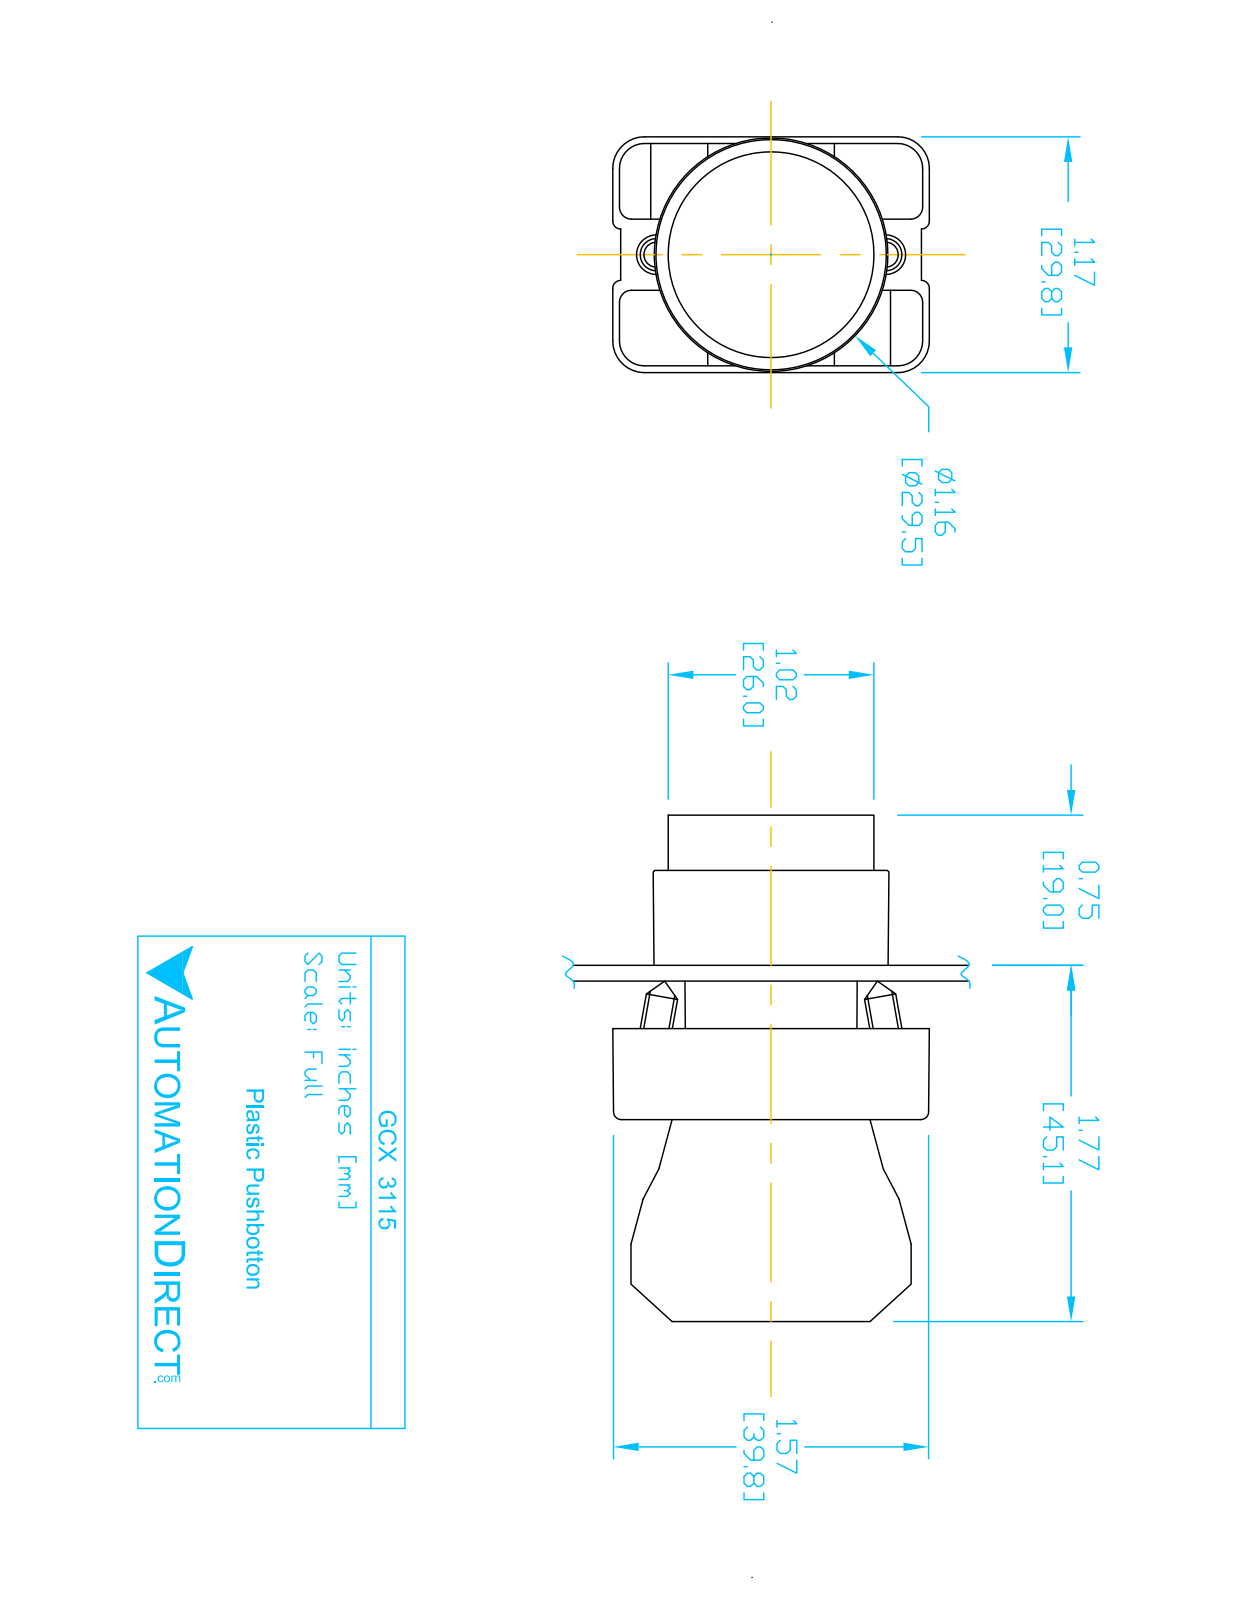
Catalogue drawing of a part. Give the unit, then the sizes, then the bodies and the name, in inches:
Units: inches
Overall size (bounding box): 2.492 × 1.581 × 1.177
Round holes (diameter × count): ⌀0.079 ×2, ⌀0.124 ×2, ⌀0.13 ×2, ⌀0.087 ×1, ⌀0.197 ×1, ⌀0.878 ×1, ⌀0.888 ×1, ⌀1.024 ×1
Round bosses / shafts (diameter × count): ⌀0.157 ×2, ⌀1.175 ×1, ⌀1.004 ×1, ⌀0.945 ×1, ⌀0.856 ×1, ⌀0.78 ×1
Partial cylindrical surfaces — rounded edges, fillets, slot ends (radius × count): R0.059 ×24, R0.041 ×12, R0.124 ×12, R0.157 ×12, R0.039 ×4, R0.128 ×2, R0.02 ×1, R0.063 ×1
Main face-to-face distances: 0.579, 0.033, 1.193, 0.031, 0.472, 0.72, 0.276, 0.689, 0.598, 1.161
Hole centre spacings: 0.236, 0.544, 0.472, 0.49
Volume: 1.584 in³ · Surface area: 26.47 in²
Bodies: 6 solids, 383 faces (222 planar, 132 cylindrical, 29 other)
Part name (STEP PRODUCT): ECX3029-2; ecx1040; GCX3115 OPERATOR; GCX3115
STEP written by: SolidWorks 2016 (AUTOMOTIVE_DESIGN)
